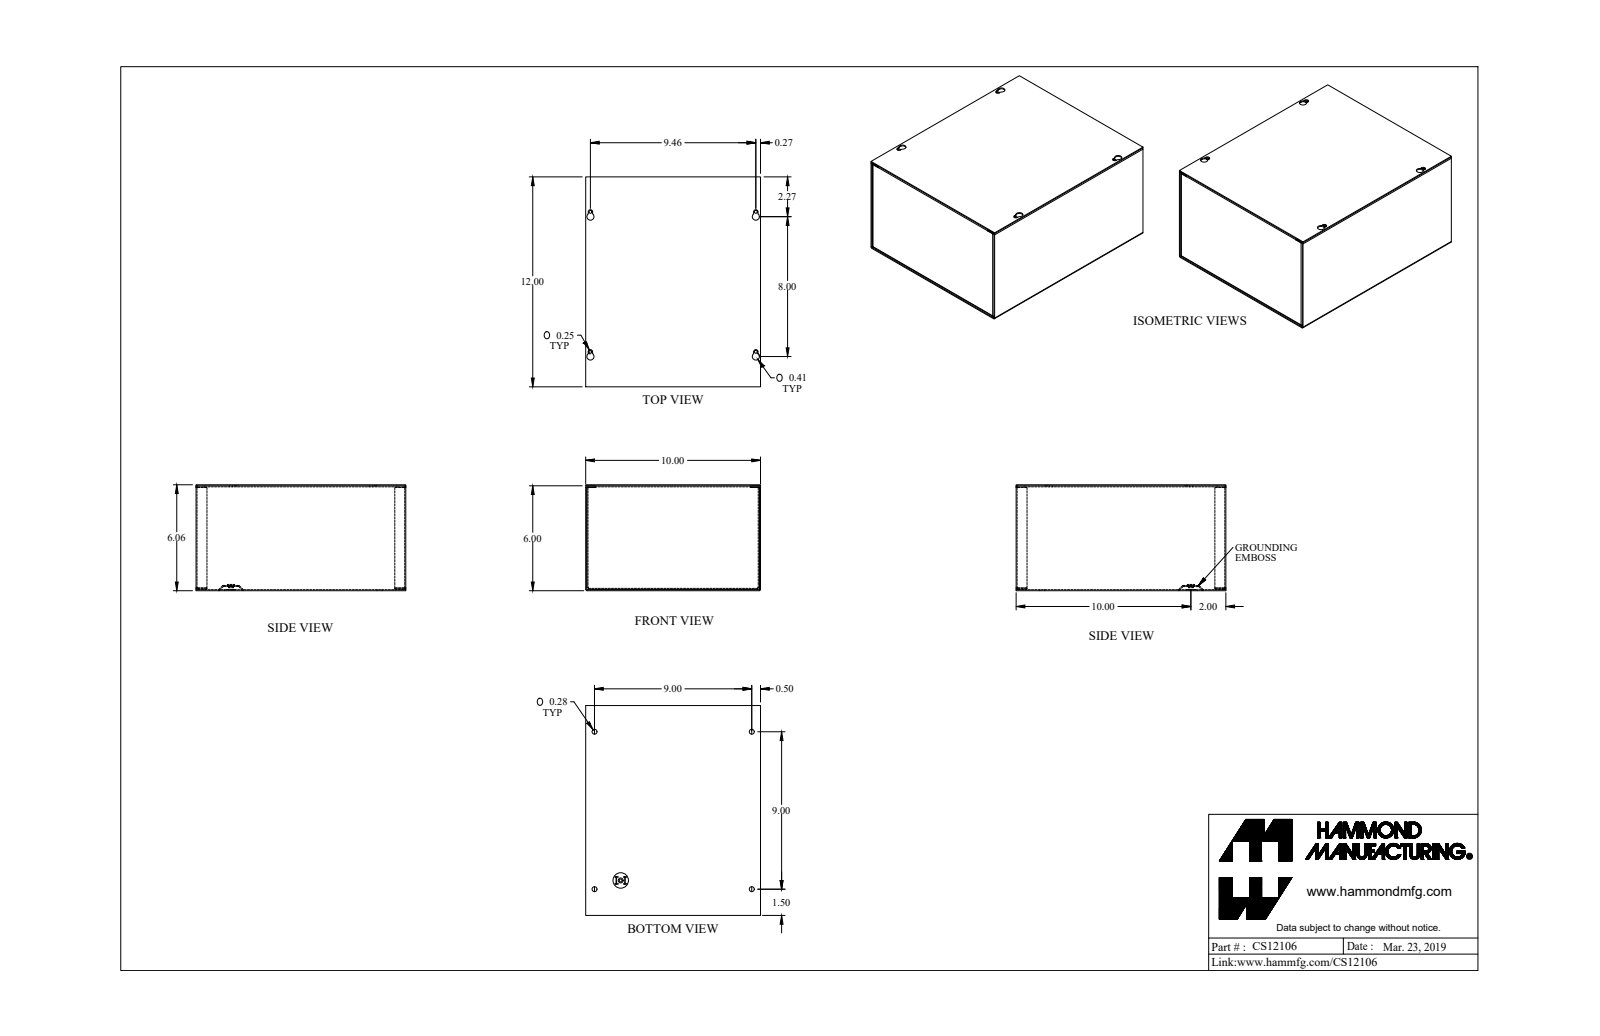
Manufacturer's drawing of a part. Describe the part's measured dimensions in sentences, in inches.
The part is named "CS12106_Default". Its 3-D file was written by "SolidWorks 2019 (CONFIG_CONTROL_DESIGN)". It is 4 solids with 205 faces: 125 planar, 72 cylindrical and 8 other. Overall it measures 12 by 10 by 6.057 inches. Its volume is 30.69 cubic inches and its surface area 1 088 square inches. Round holes: 5 of diameter 0.17, 4 of diameter 0.281, 1 of diameter 0.5. Round bosses or shafts: 1 of diameter 0.492, 1 of diameter 0.284. Partial cylindrical surfaces (rounded edges, fillets, slot ends): 12 of radius 0.029, 12 of radius 0.086, 8 of radius 0.057, 4 of radius 0.125, 4 of radius 0.203. The main face-to-face distances are 0.057, 6, 9.943, 5.943, 6.057, 11.943, 10, 9.886, 12, 11.886. The hole center spacings are 0.55, 8.503, 9, 9.243, 12.548, 8, 9.46, 12.389.
